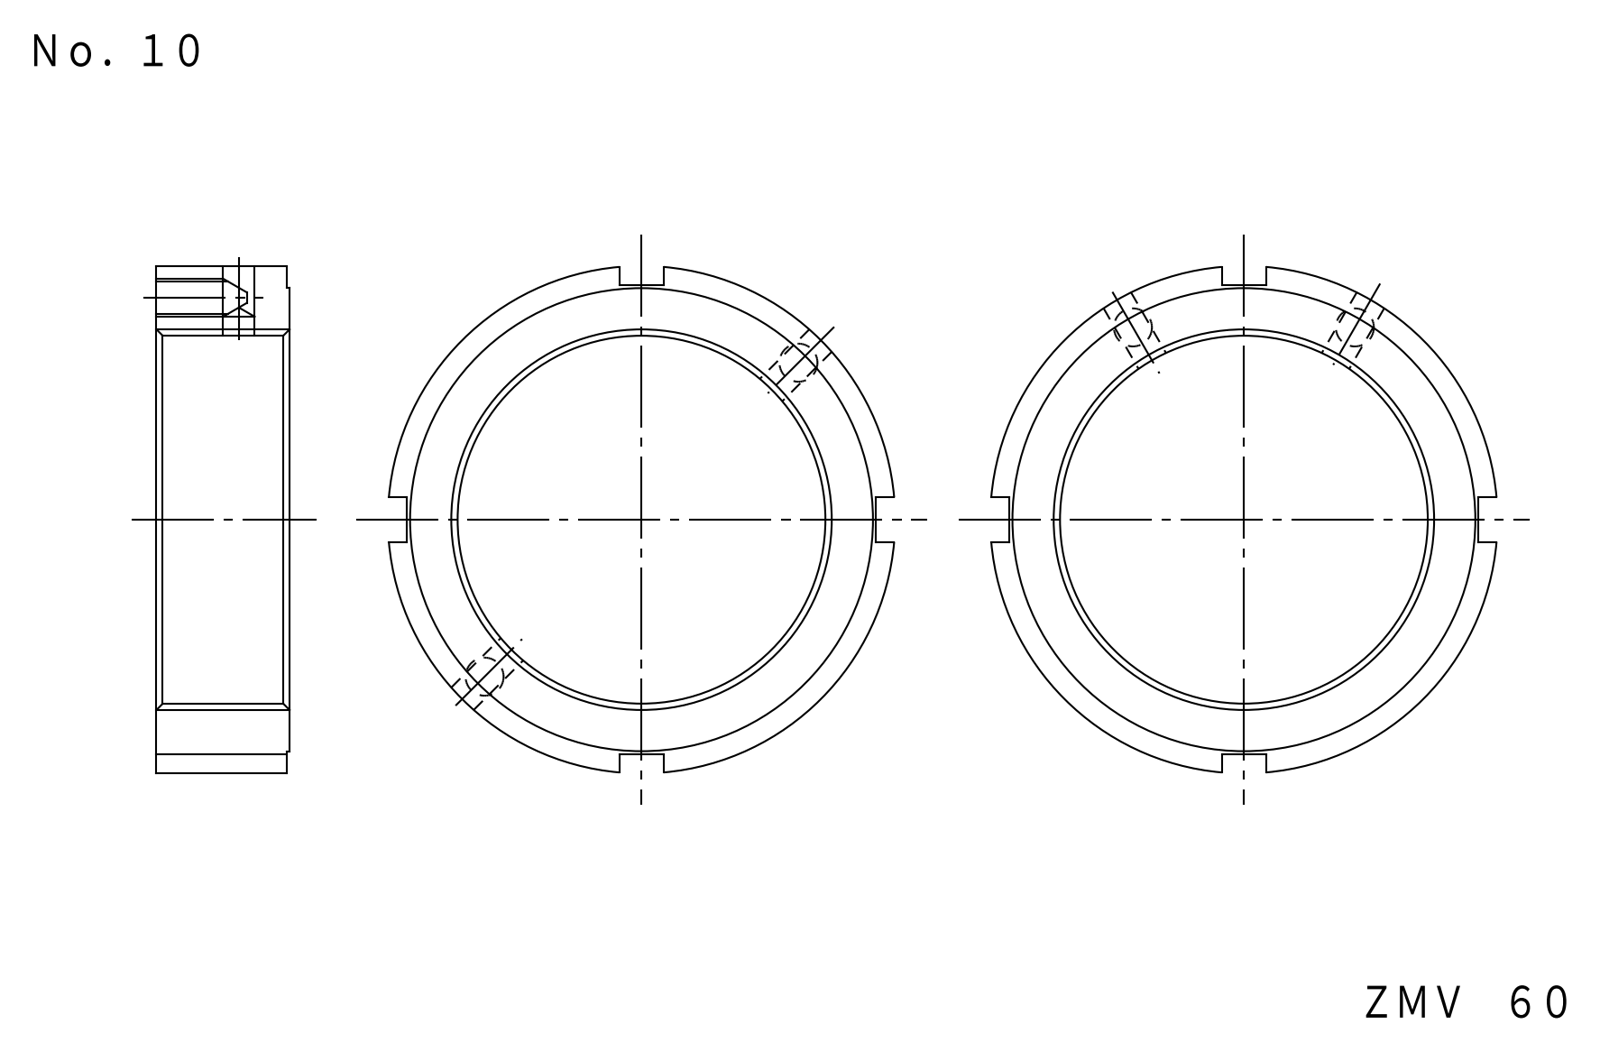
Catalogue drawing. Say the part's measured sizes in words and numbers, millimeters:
The part is named "FKD ZMV60". Its 3-D file was written by "Autodesk Inventor LT (CONFIG_CONTROL_DESIGN)". It is 1 solid with 25 faces: 15 planar, 10 cylindrical and 0 other. Overall it measures 79.69 by 79.69 by 21 millimeters. Its volume is 43 263 cubic millimeters and its surface area 14 426 square millimeters. Round holes: 2 of diameter 4.92, 2 of diameter 5, 1 of diameter 60. Round bosses or shafts: 1 of diameter 80, 1 of diameter 73. The main face-to-face distances are 21, 0.5, 20.5, 33.5, 40.5, 74, 7. The hole center spacings are 35, 70.
